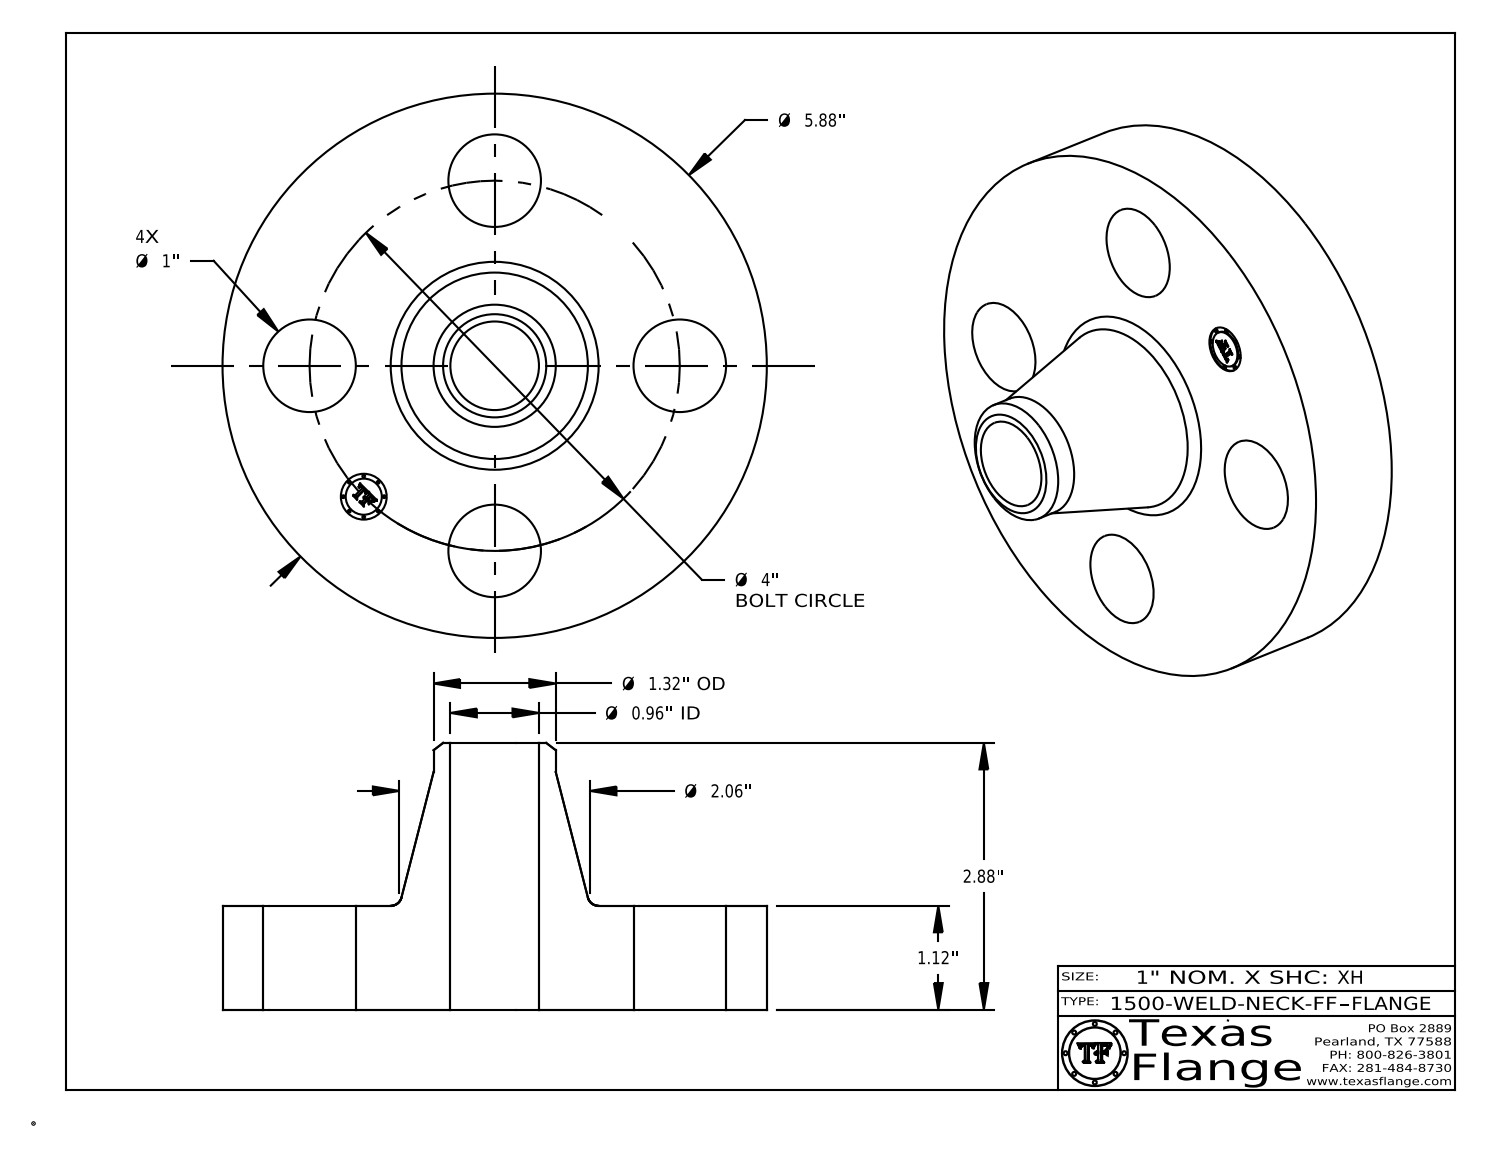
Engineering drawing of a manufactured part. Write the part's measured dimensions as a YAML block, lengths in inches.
part_name: "1500-WELD-NECK-FF"
step_written_by: "CATIA V5 STEP AP214 (AUTOMOTIVE_DESIGN)"
units: inches
bodies: {solids: 1, faces: 408, planar: 368, cylindrical: 34, other: 6}
overall_size: [5.88, 5.88, 2.88]
volume: 28.54
surface_area: 96.96
round_holes:
  - {diameter: 1, count: 4}
  - {diameter: 0.495, count: 1}
  - {diameter: 0.957, count: 1}
round_bosses_or_shafts:
  - {diameter: 0.03, count: 8}
  - {diameter: 5.88, count: 1}
  - {diameter: 1.32, count: 1}
  - {diameter: 0.39, count: 1}
face_to_face_distances: [1.12, 2.88, 1.76, 0.015, 1.105, 1.775, 0.148, 0.145, 0.027, 0.096]
hole_center_spacings: [2, 2.828, 1.531, 3.695, 4]
